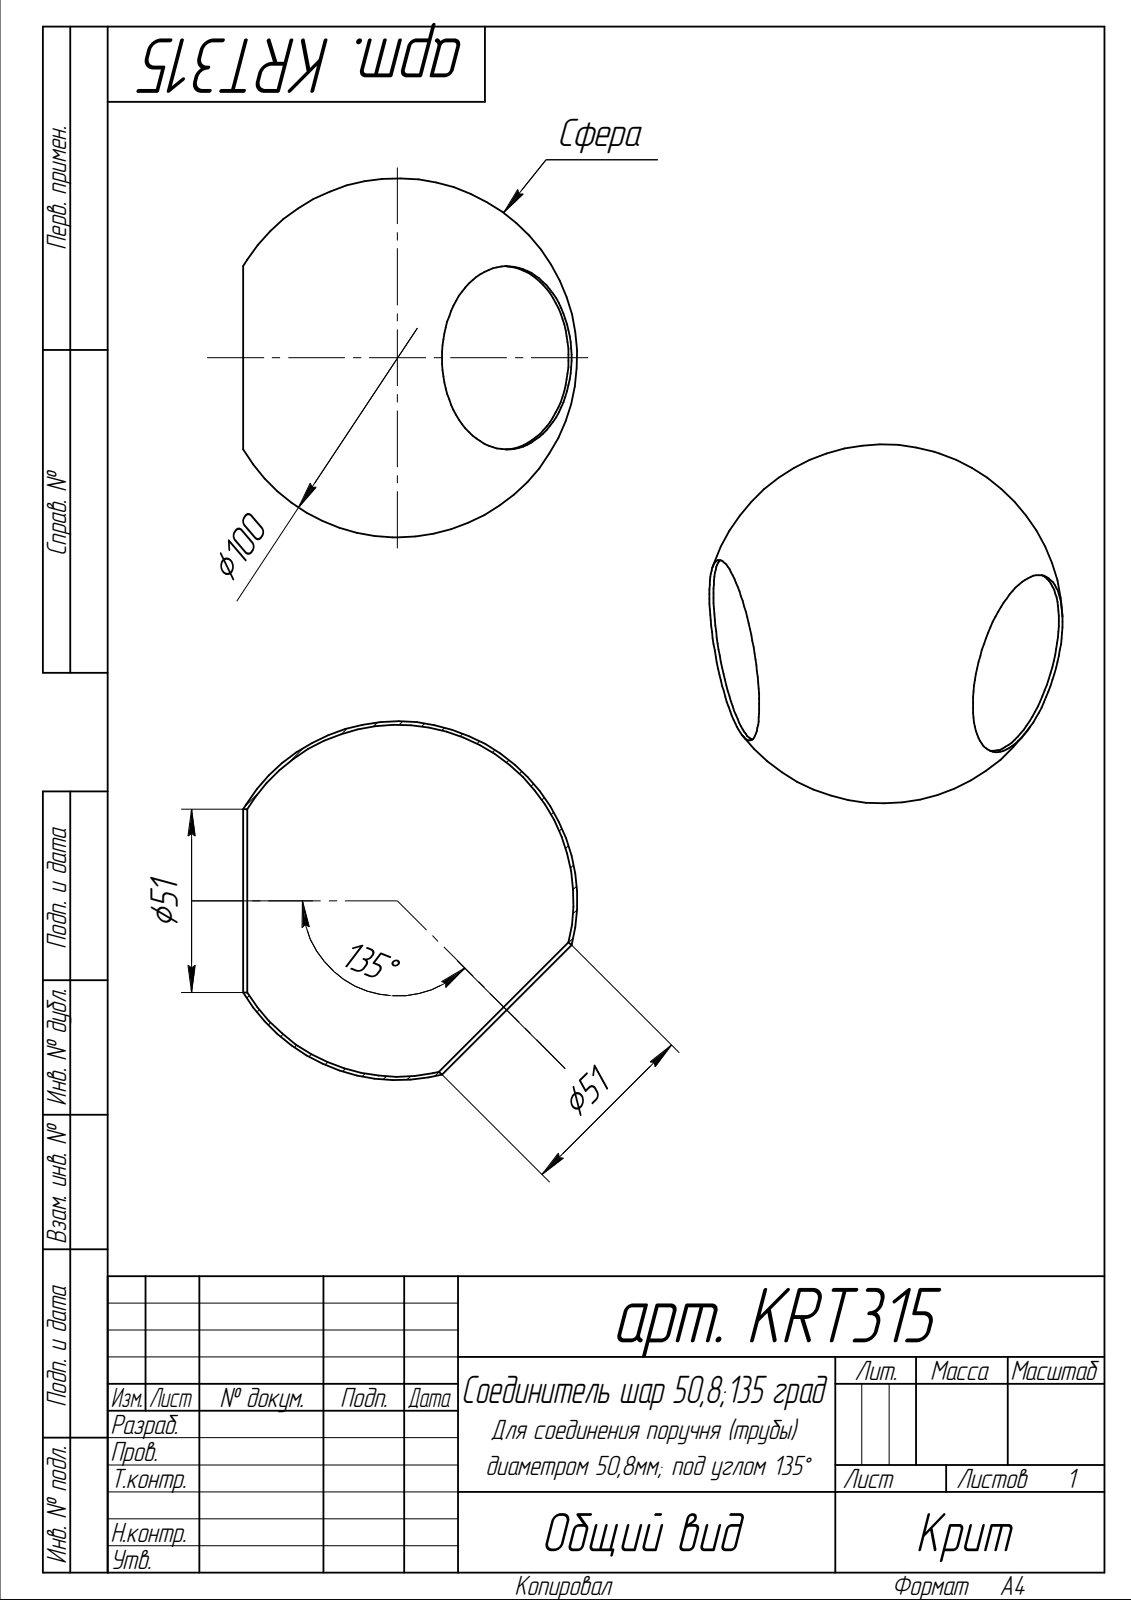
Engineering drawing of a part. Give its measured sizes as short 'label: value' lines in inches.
name: арт. KRT315
written by: SolidWorks 2014 (AUTOMOTIVE_DESIGN)
unit: in
bodies: 1 solid, 8 faces (0 planar, 4 cylindrical, 4 other)
size: 3.937 × 3.937 × 3.662
volume: 1.611 in³; area: 82.4 in²
holes: 2× ⌀2.008
